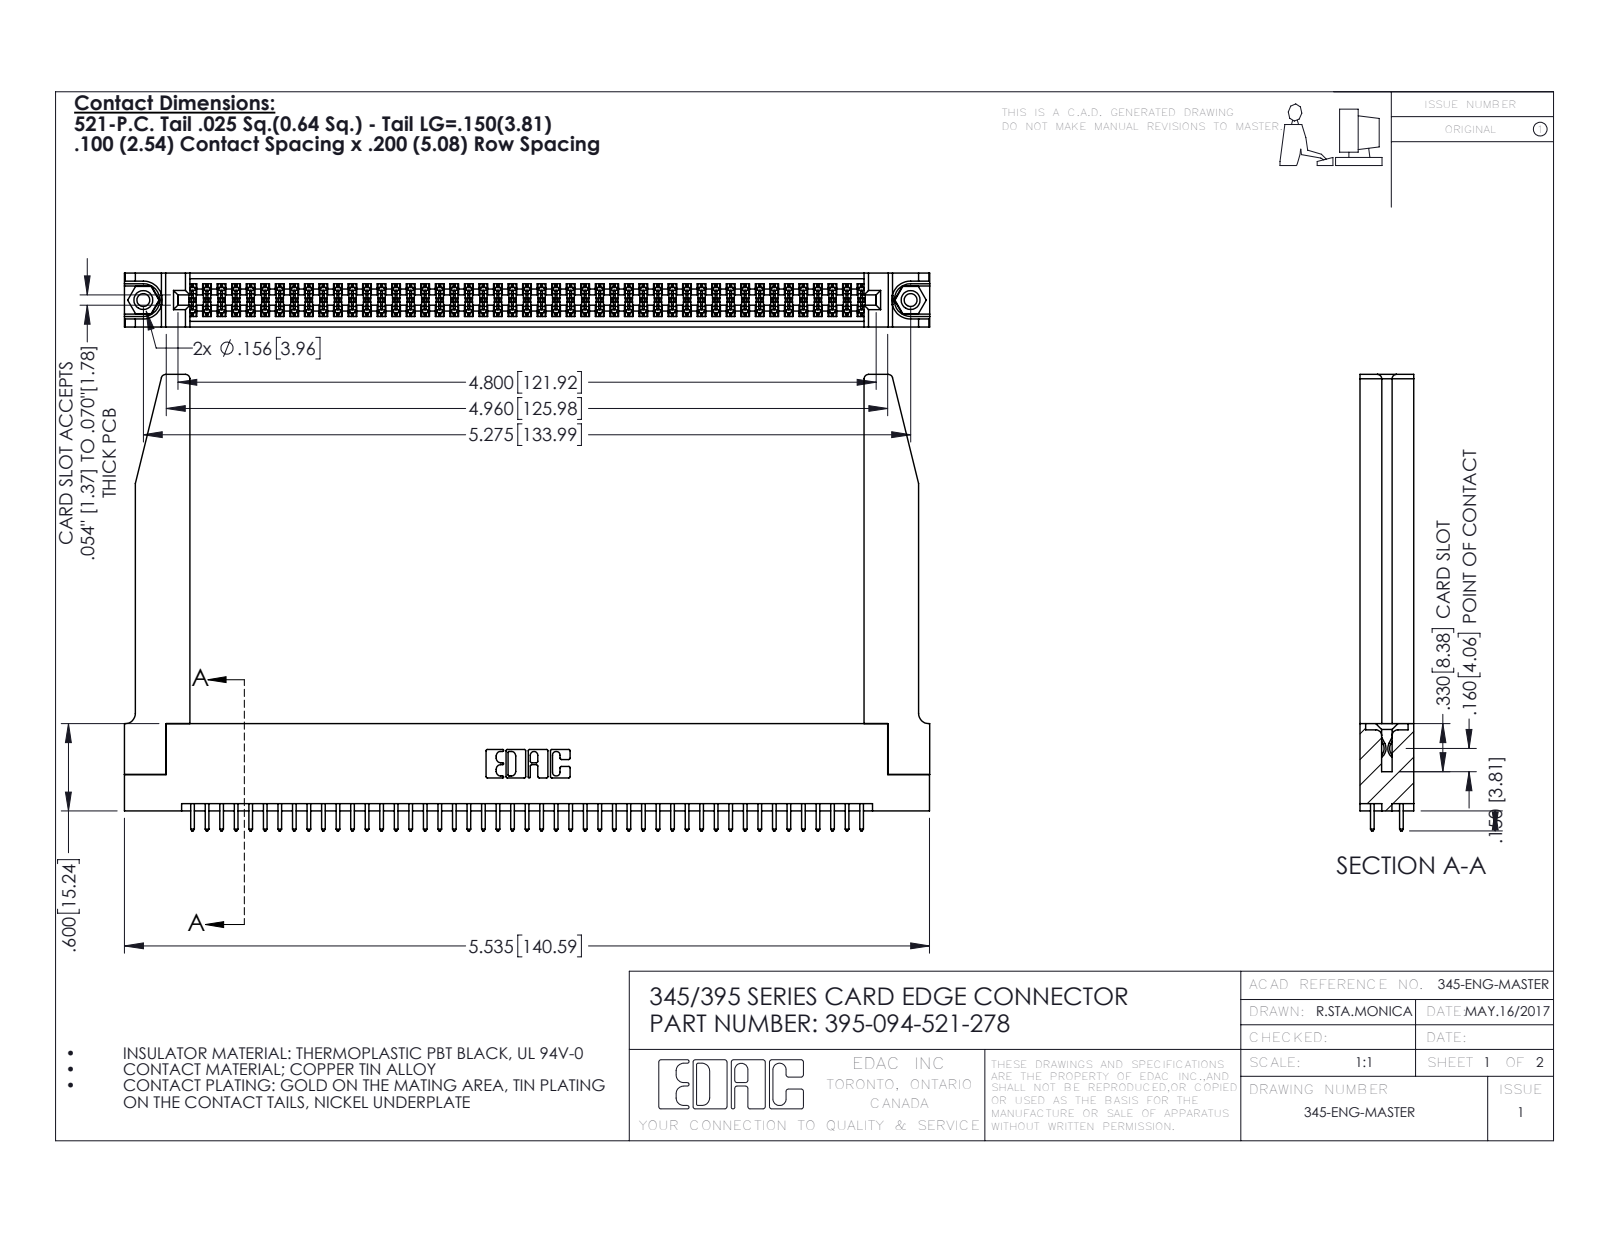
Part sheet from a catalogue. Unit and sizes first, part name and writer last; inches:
Units: inches
Overall size (bounding box): 5.536 × 3.137 × 0.37
Round holes (diameter × count): ⌀0.089 ×2, ⌀0.125 ×2, ⌀0.156 ×2, ⌀0.064 ×1
Round bosses / shafts (diameter × count): ⌀0.155 ×2
Partial cylindrical surfaces — rounded edges, fillets, slot ends (radius × count): R0.006 ×141, R0.01 ×94, R0.01 ×22, R0.03 ×8, R0.007 ×6, R0.031 ×6, R0.026 ×3, R0.014 ×2
Main face-to-face distances: 0.072, 0.37, 0.298, 0.2, 0.098, 0.272, 0.025, 0.225, 0.175, 0.148
Hole centre spacings: 0.27, 5.039, 5.275
Volume: 1.308 in³ · Surface area: 41.68 in²
Bodies: 99 solids, 5060 faces (3324 planar, 1684 cylindrical, 52 other)
Part name (STEP PRODUCT): 345-220-078_345-220-078; 395-094-521-278; 345 Part_Flush Mounting Lugs - 0.156 Dia-TH; 345-250-001_345-250-001-102 (+1 more)
STEP written by: SolidWorks 2016 (CONFIG_CONTROL_DESIGN)
